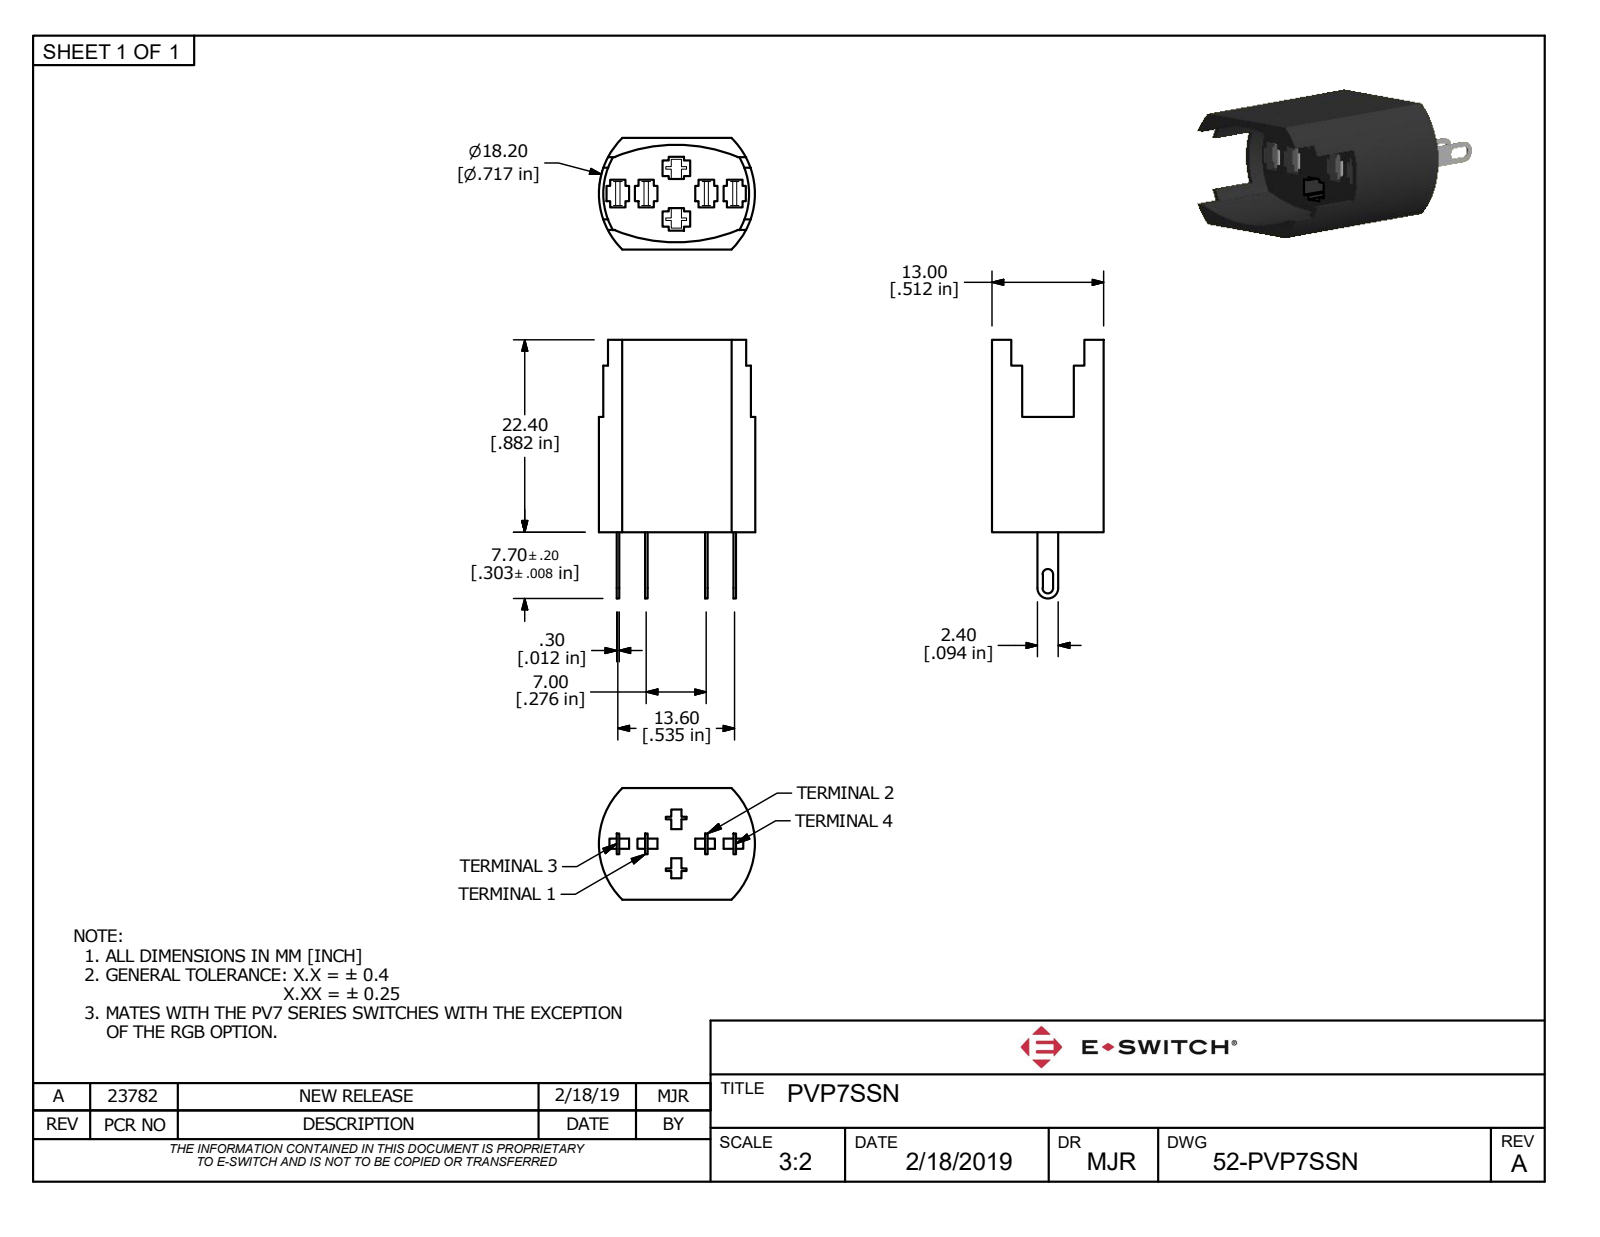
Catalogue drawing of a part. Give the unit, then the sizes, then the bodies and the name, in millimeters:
Units: millimetres
Overall size (bounding box): 30.1 × 18.2 × 13
Partial cylindrical surfaces — rounded edges, fillets, slot ends (radius × count): R0.25 ×8, R0.6 ×2, R18.8 ×2, R1.2 ×1, R8.47 ×1, R9.1 ×1
Main face-to-face distances: 13, 3.3, 0.4, 10.3, 11.3, 3.2, 3.7, 2.9, 3.4, 0.5
Volume: 2 672 mm³ · Surface area: 2 668 mm²
Bodies: 1 solid, 227 faces (201 planar, 26 cylindrical, 0 other)
Part name (STEP PRODUCT): PVP7SSN
STEP written by: Autodesk Inventor 2018 (AP242_MANAGED_MODEL_BASED_3D_ENGINEERING_MIM_LF)
